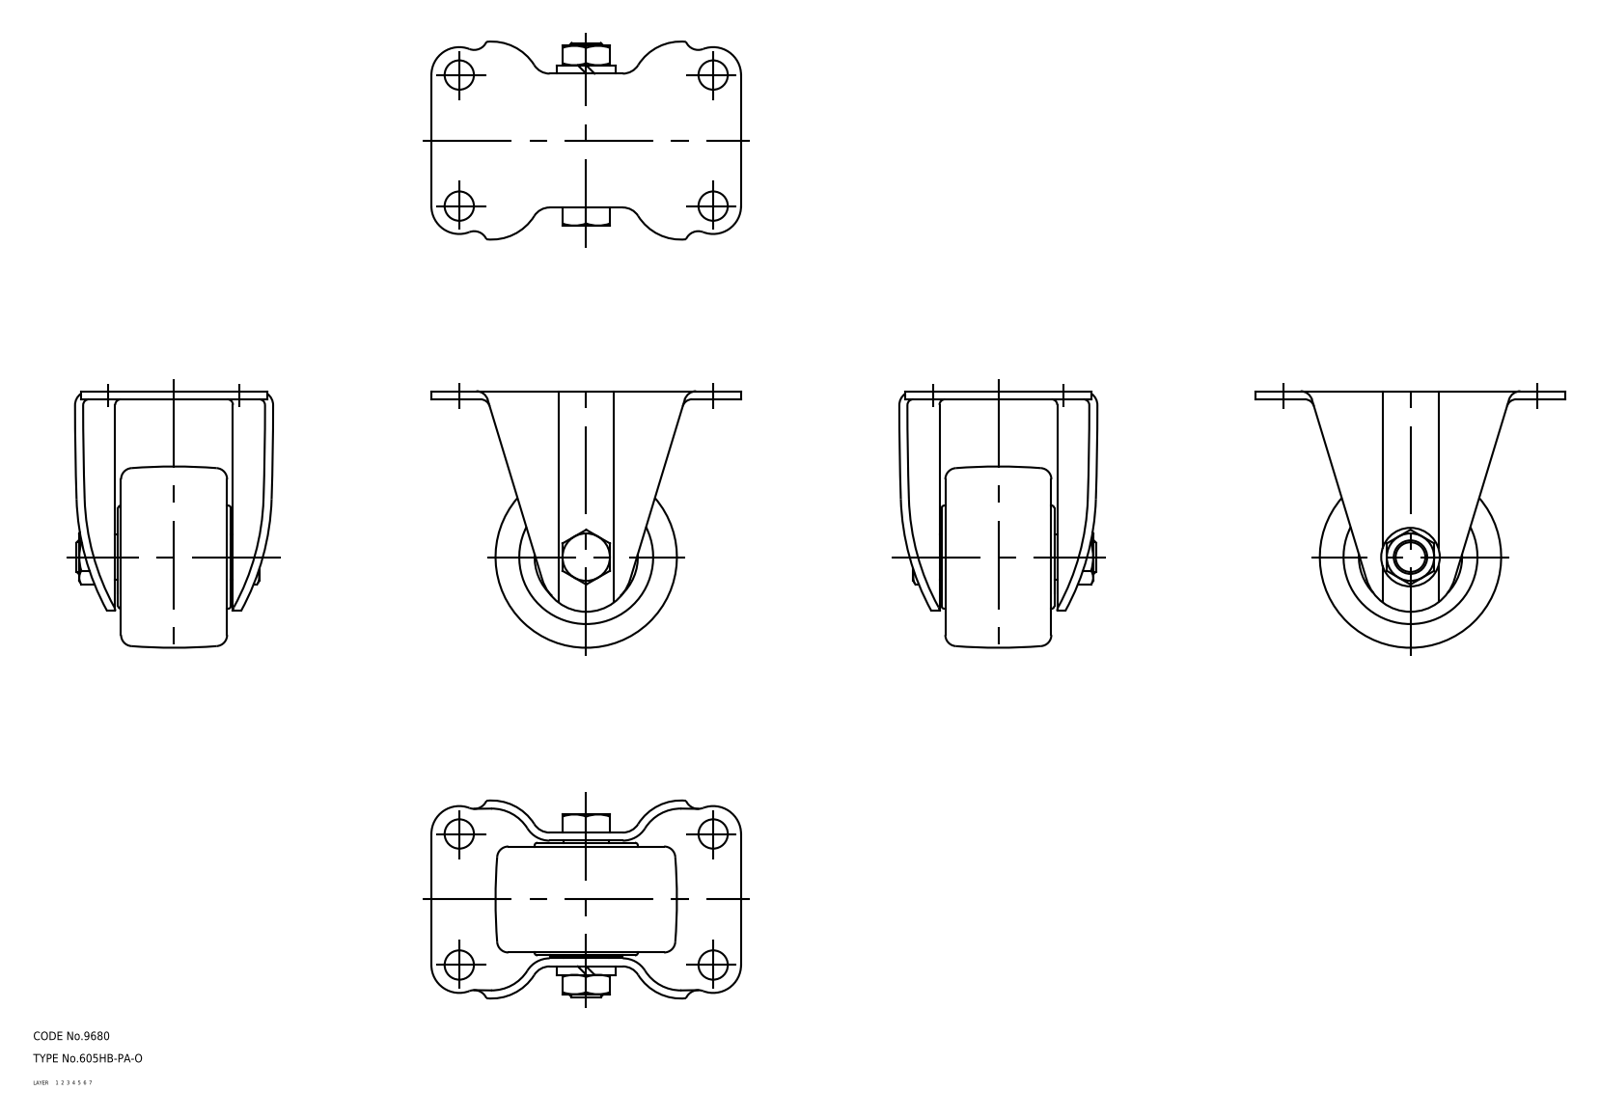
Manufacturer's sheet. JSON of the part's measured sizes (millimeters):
{"part_name": "67119343; 67119356; 67119369", "step_written_by": "CADfix (AUTOMOTIVE_DESIGN)", "units": "millimeters", "bodies": {"solids": 3, "faces": 160, "planar": 0, "cylindrical": 0, "other": 160}, "overall_size": [111, 92, 71], "volume_mm3": 170508, "surface_area_mm2": 48773}
